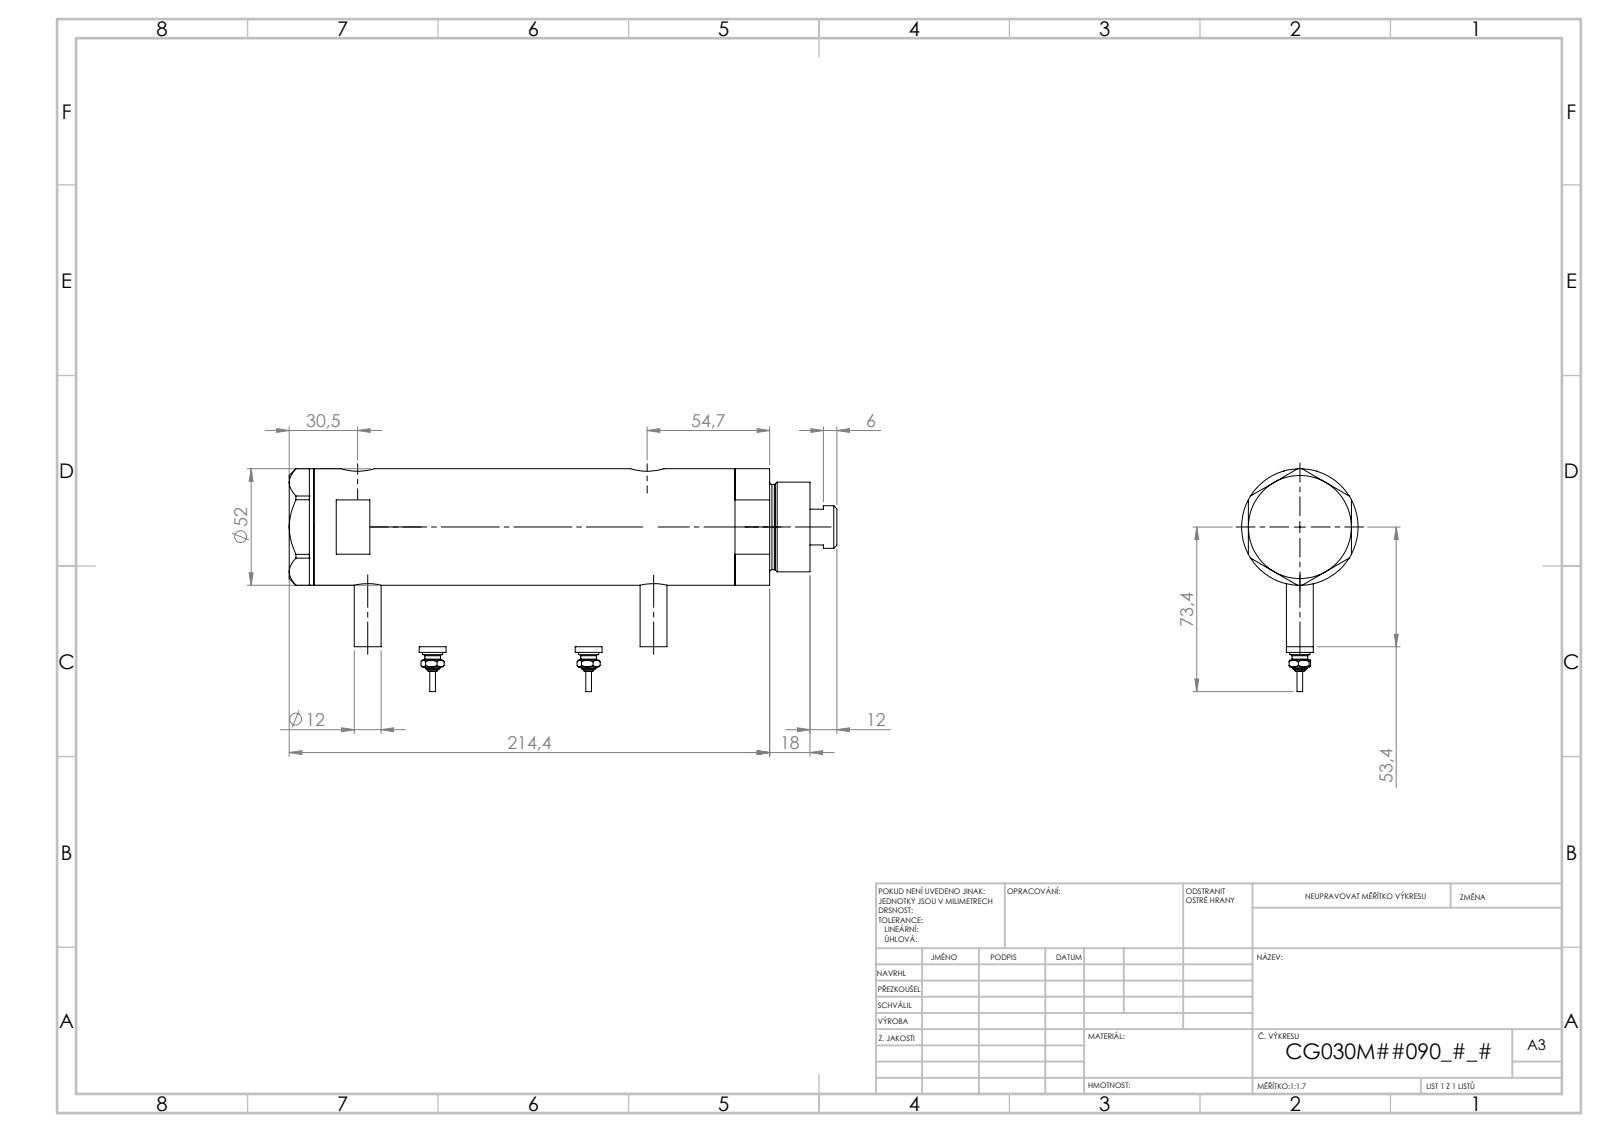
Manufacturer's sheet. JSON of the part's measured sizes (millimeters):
{"part_name": "V270CG_BACK; V270CG_VC; V270CG_MIDDLE; V270CG_SWITCH (+1 more)", "step_written_by": "SolidWorks 2019 (CONFIG_CONTROL_DESIGN)", "units": "millimeters", "bodies": {"solids": 6, "faces": 246, "planar": 95, "cylindrical": 77, "other": 74}, "overall_size": [239.02, 84.3, 52], "volume_mm3": 426167, "surface_area_mm2": 95876, "round_holes": [[5, 2], [9.73, 2], [12.5, 2], [15, 2], [6.5, 1], [20, 1], [21.5, 1], [30, 1], [33, 1], [44, 1]], "round_bosses_or_shafts": [[12, 2], [9, 2], [7, 2], [5, 2], [4.34, 2], [2.4, 2], [52, 1], [40, 1]], "face_to_face_distances": [143.54, 23.8, 119.74, 11, 34.8, 154.54, 46, 190.94, 179.94, 156.14], "hole_center_spacings": [2.9, 4.5, 116.75, 119.65, 121.25, 124.15, 2.89, 2.91]}
